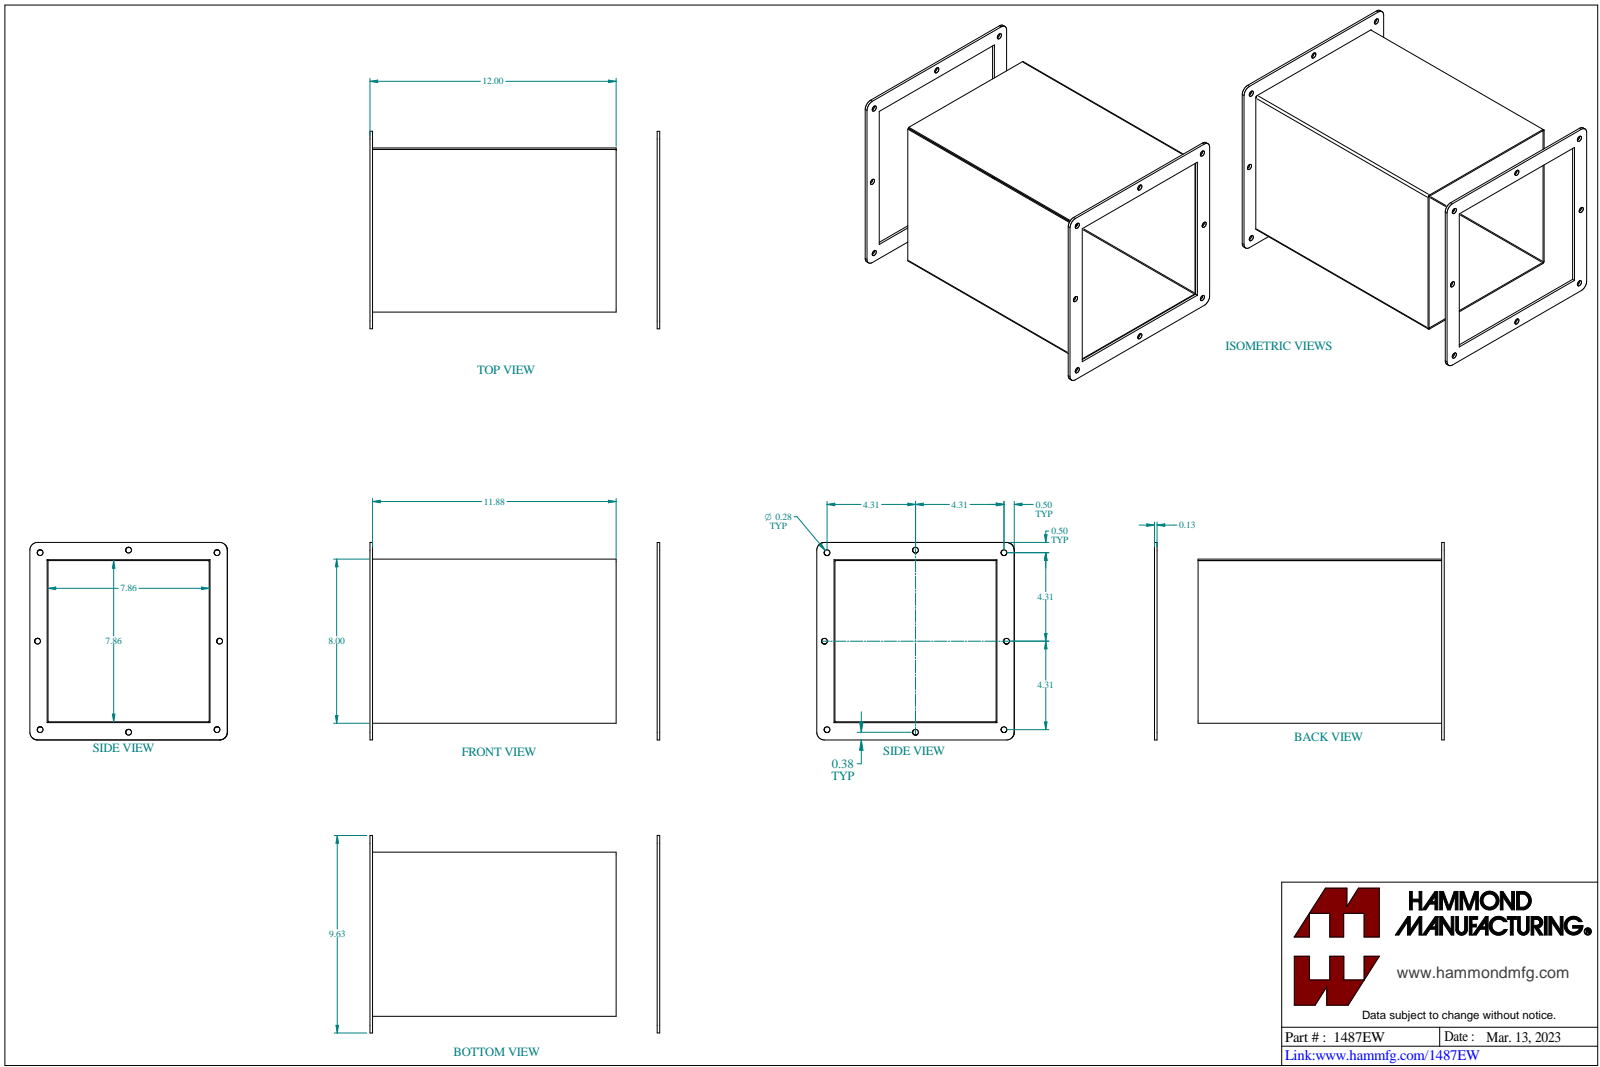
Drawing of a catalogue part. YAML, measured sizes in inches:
part_name: "1487EW"
step_written_by: "SolidWorks 2023 (CONFIG_CONTROL_DESIGN)"
units: inches
bodies: {solids: 4, faces: 112, planar: 42, cylindrical: 70, other: 0}
overall_size: [14.25, 9.628, 9.628]
volume: 37.85
surface_area: 958.2
round_holes:
  - {diameter: 0.281, count: 16}
partial_cylinders:
  - {radius: 0.375, count: 8}
  - {radius: 0.25, count: 4}
  - {radius: 0.036, count: 3}
  - {radius: 0.108, count: 3}
face_to_face_distances: [0.072, 7.928, 8, 7.856, 0.125, 14, 0.25, 0.125, 14.125, 14.25]
hole_center_spacings: [4.315, 9.755, 6.276, 8.625, 12.198, 4.311, 4.311, 4.317]
